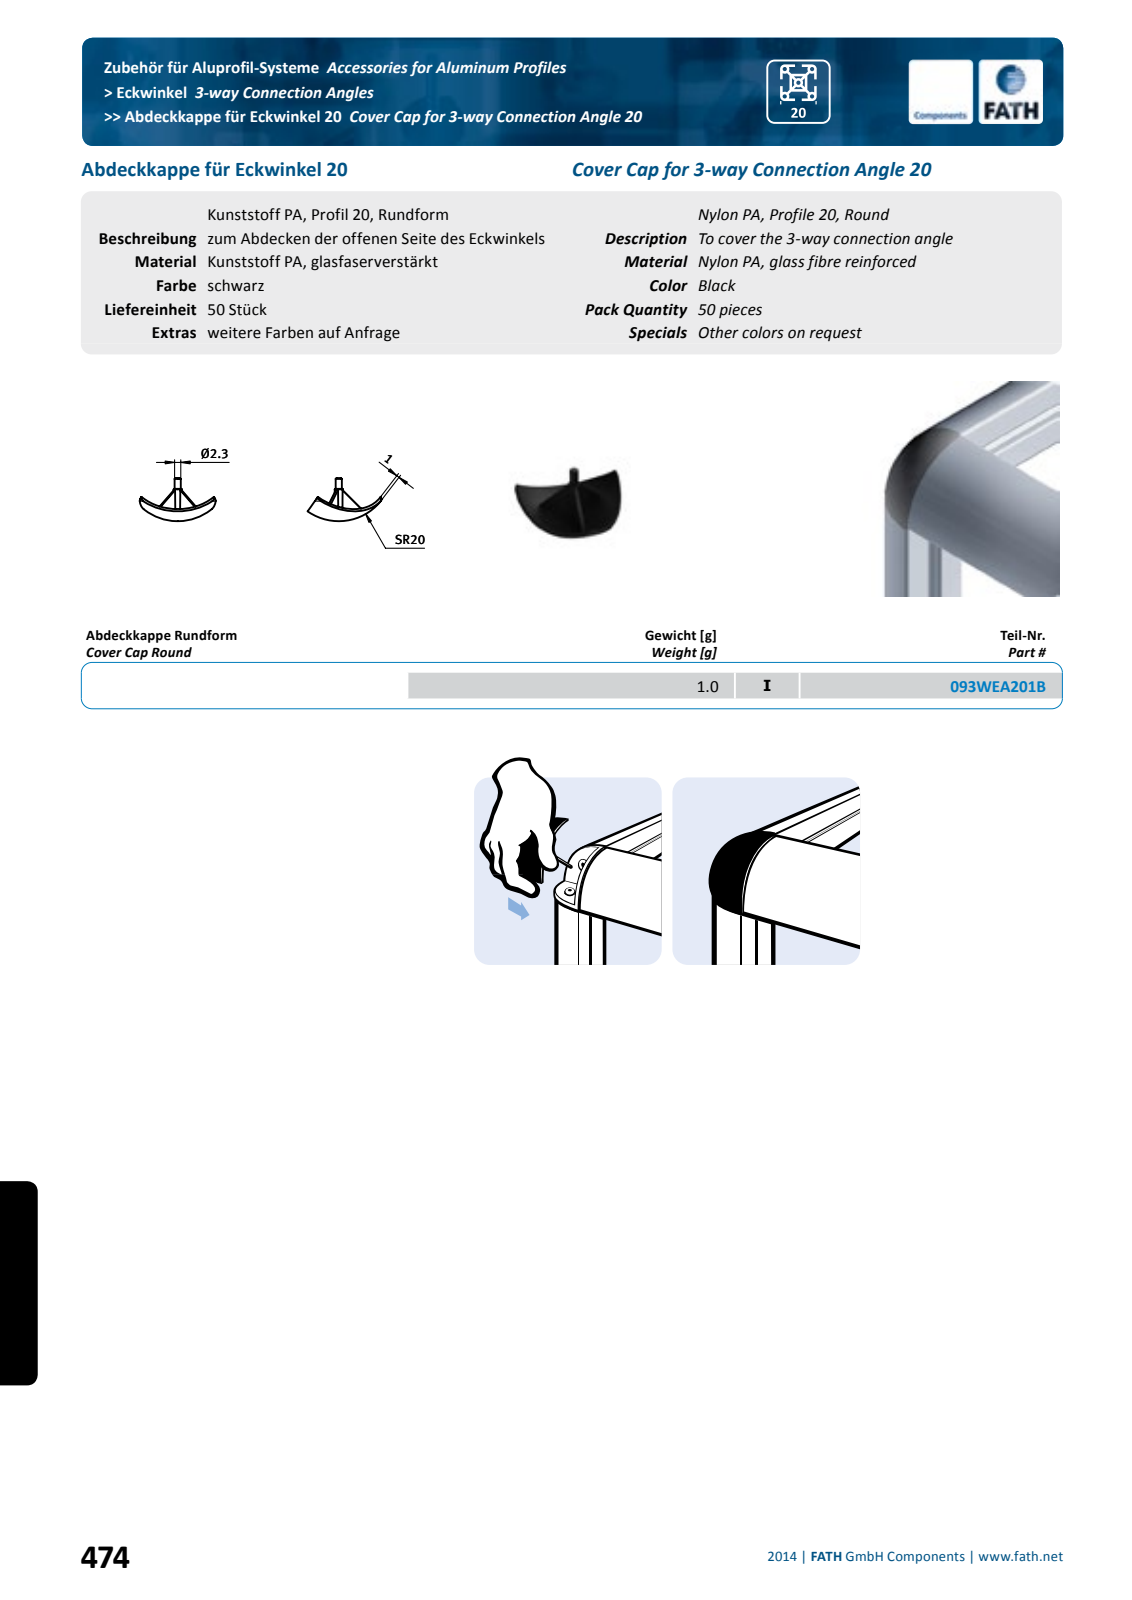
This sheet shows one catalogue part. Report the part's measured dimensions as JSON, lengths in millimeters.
{"part_name": "fath_093wea201b", "step_written_by": "Spatial InterOp 3D (automotive_design)", "units": "millimeters", "bodies": {"solids": 1, "faces": 61, "planar": 17, "cylindrical": 12, "other": 32}, "overall_size": [28.19, 20, 19.96], "volume_mm3": 836, "surface_area_mm2": 1645, "round_bosses_or_shafts": [[3, 1], [2.3, 1]], "partial_cylinders_radius": [[0.2, 6]], "face_to_face_distances": [4]}
